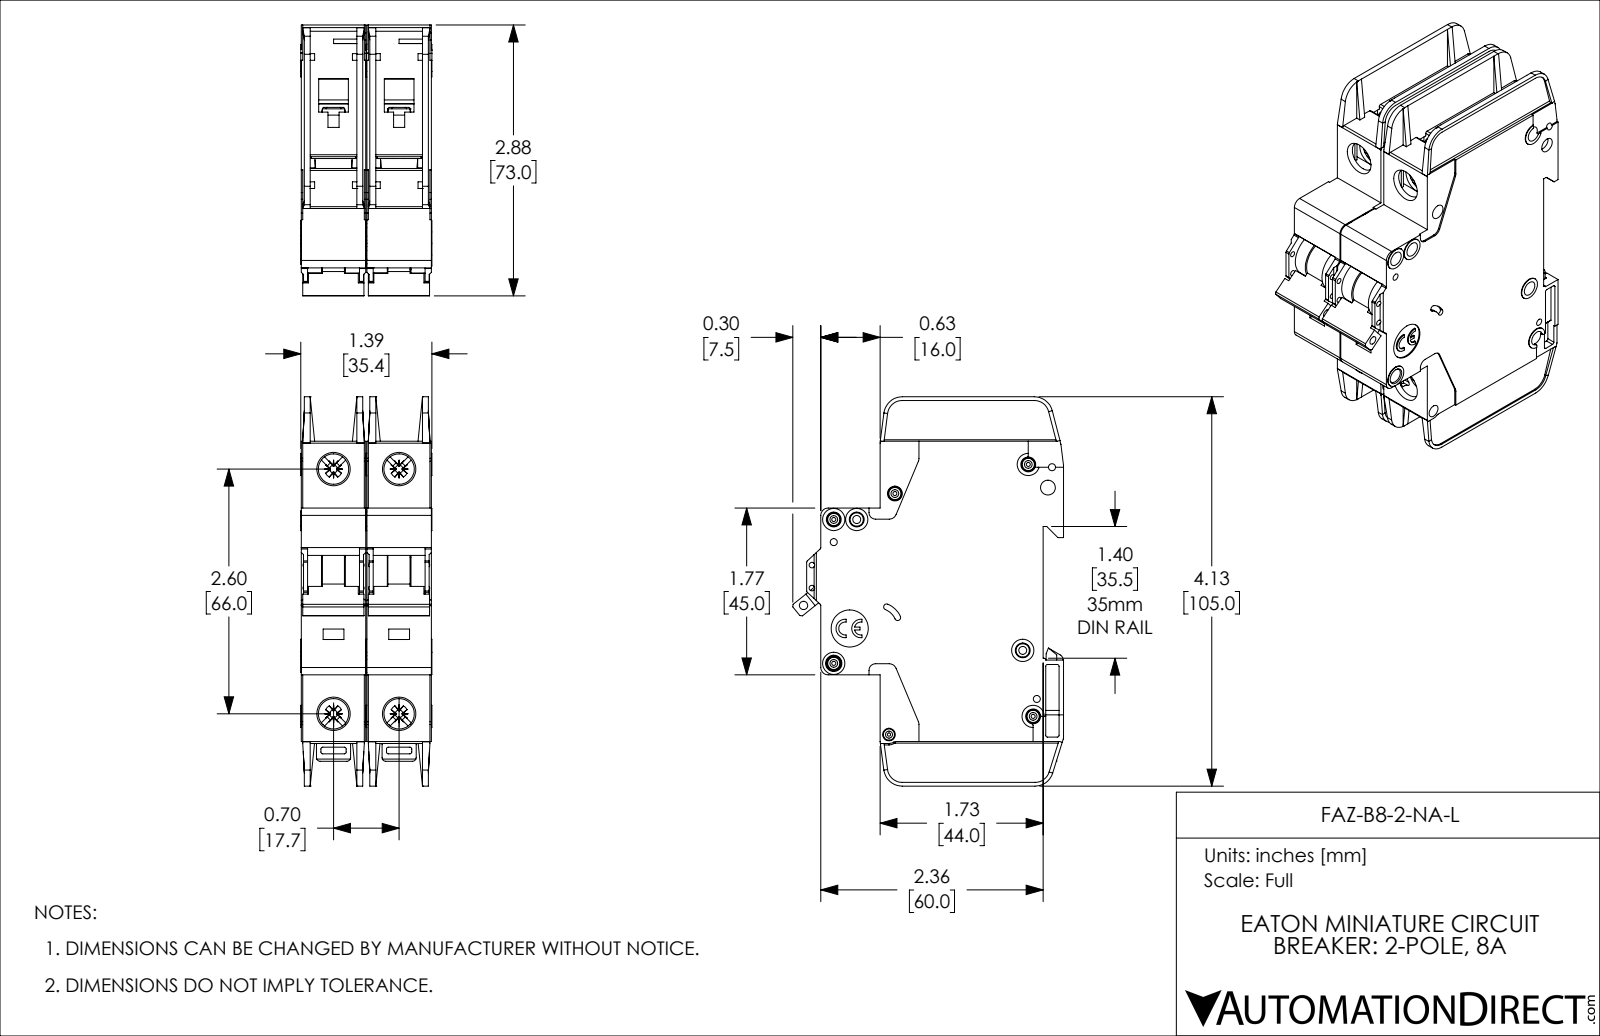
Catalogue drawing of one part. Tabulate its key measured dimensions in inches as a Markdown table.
| quantity | value |
| --- | --- |
| part name | FAZ-B8-2-NA-L |
| STEP written by | SolidWorks 2019 (AUTOMOTIVE_DESIGN) |
| units | inches |
| bodies | 2 solids, 2254 faces (1342 planar, 714 cylindrical, 198 other) |
| overall size | 4.134 × 2.876 × 1.394 |
| volume | 9.365 in³ |
| surface area | 82.01 in² |
| round holes (diameter × count) | 0.157 × 8, 0.043 × 5, 0.075 × 4, 0.323 × 4, 0.059 × 2, 0.085 × 2, 0.035 × 1, 0.089 × 1, 0.098 × 1, 0.134 × 1, 0.394 × 1 |
| round bosses / shafts (diameter × count) | 0.13 × 5, 0.236 × 4, 0.118 × 3, 0.098 × 2 |
| partial cylindrical surfaces (radius × count) | 0.02 × 57, 0.016 × 20, 0.039 × 14, 0.079 × 10, 0.043 × 8, 0.008 × 5, 0.197 × 5, 0.01 × 4 |
| main face-to-face distances | 0.697, 0.047, 0.685, 0.591, 0.094, 0.638, 0.543, 1.382, 0.744, 0.65 |
| hole center spacings | 0.244, 0.537, 0.697, 0.87, 2.598, 2.69, 0.189, 0.199 |
